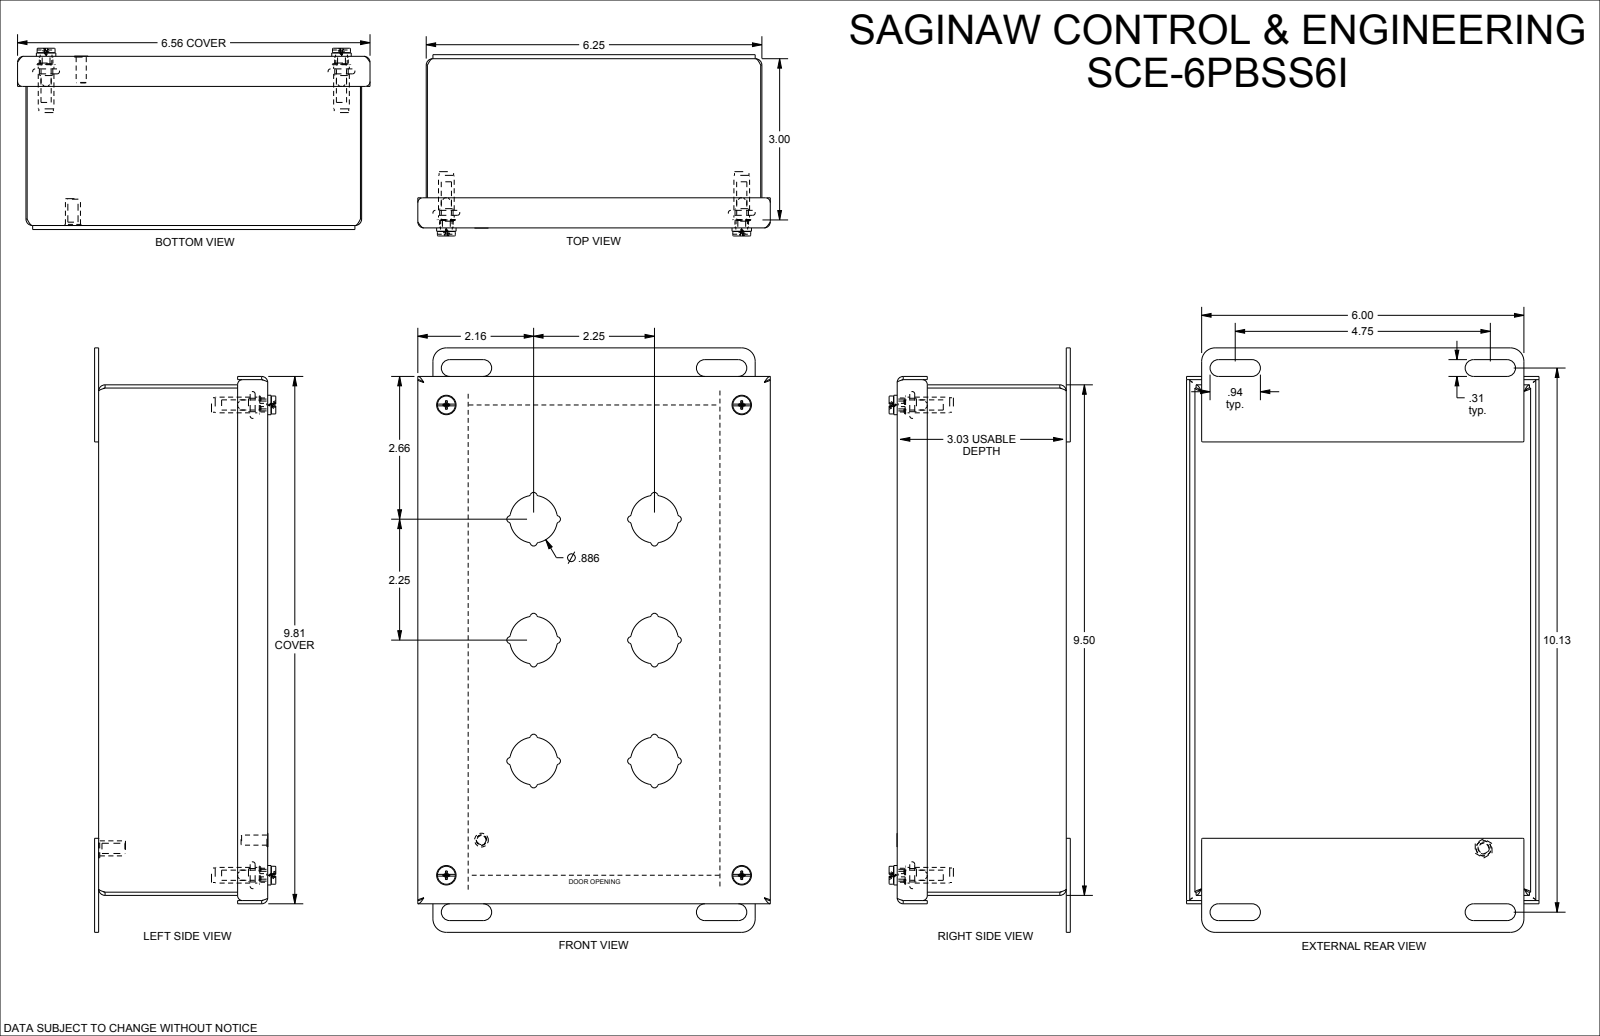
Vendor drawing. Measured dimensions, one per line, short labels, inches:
name: SCE-6PBSSI
written by: SolidWorks 2021 (AUTOMOTIVE_DESIGN)
unit: in
bodies: 3 solids, 514 faces (154 planar, 276 cylindrical, 84 other)
size: 10.875 × 6.563 × 3.286
volume: 16.52 in³; area: 522.2 in²
holes: 5× ⌀0.19, 4× ⌀0.22, 4× ⌀0.25, 4× ⌀0.266, 4× ⌀0.317
bosses: 4× ⌀0.362, 4× ⌀0.34, 4× ⌀0.292, 4× ⌀0.27, 4× ⌀0.26, 1× ⌀0.28, 1× ⌀0.256, 1× ⌀0.188
rounds: 48× R0.04, 24× R0.062, 20× R0.06, 8× R0.015, 8× R0.115, 8× R0.156, 8× R0.245, 6× R0.443
face distances: 0.06, 3.088, 3.028, 6.19, 3.148, 9.44, 0.156, 6.25, 6.13, 0.075
hole spacings: 10.335, 5.5, 5.5, 8.75, 8.75, 10.335, 0.7, 0.707
